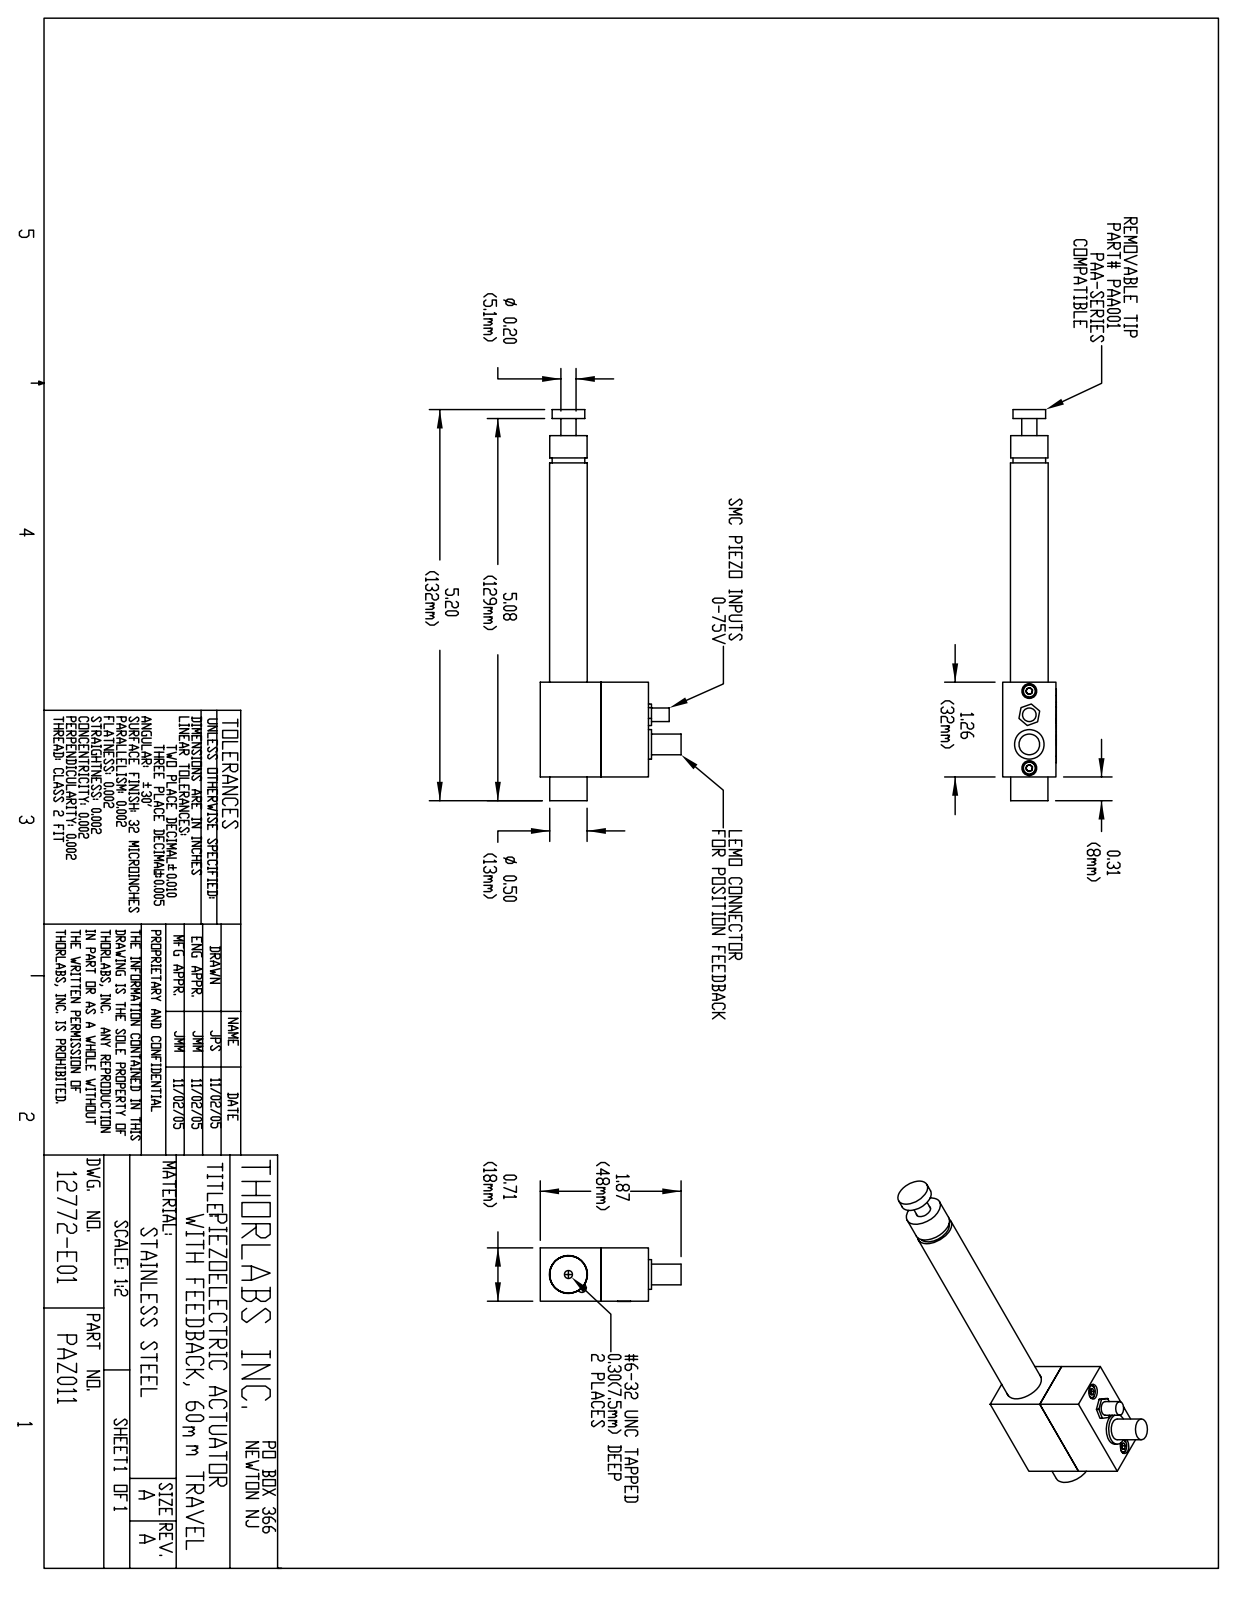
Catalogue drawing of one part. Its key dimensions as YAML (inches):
part_name: "12772-E0W"
step_written_by: "SolidWorks 2007 (AUTOMOTIVE_DESIGN)"
units: inches
bodies: {solids: 0, faces: 128, planar: 81, cylindrical: 38, other: 9}
overall_size: [5.197, 1.89, 0.771]
round_holes:
  - {diameter: 0.098, count: 2}
  - {diameter: 0.197, count: 2}
  - {diameter: 0.107, count: 1}
  - {diameter: 0.209, count: 1}
  - {diameter: 0.504, count: 1}
round_bosses_or_shafts:
  - {diameter: 0.5, count: 1}
  - {diameter: 0.496, count: 1}
  - {diameter: 0.433, count: 1}
  - {diameter: 0.394, count: 1}
  - {diameter: 0.276, count: 1}
  - {diameter: 0.201, count: 1}
  - {diameter: 0.181, count: 1}
partial_cylinders:
  - {radius: 0.087, count: 2}
  - {radius: 0.059, count: 1}
face_to_face_distances: [0.709, 1.26, 1.437, 1.575, 0.315, 3.276, 4.535, 4.85, 0.712, 0.346]
hole_center_spacings: [1.024]
